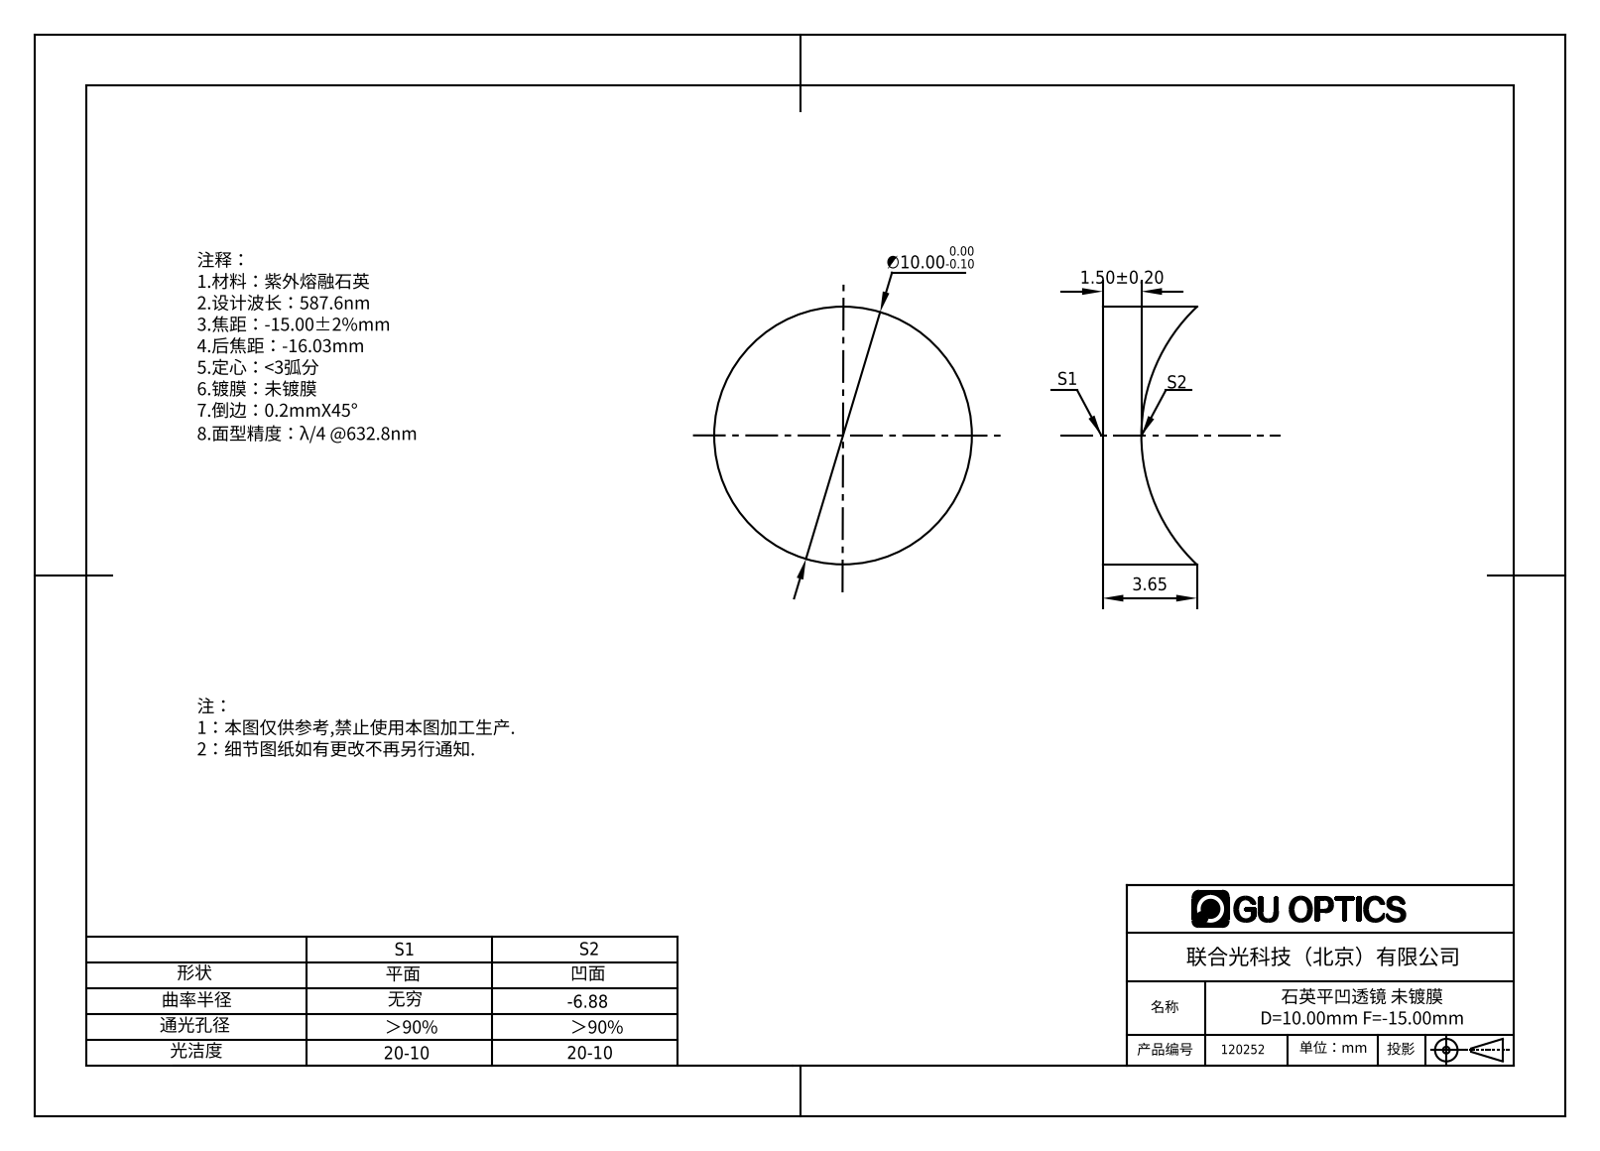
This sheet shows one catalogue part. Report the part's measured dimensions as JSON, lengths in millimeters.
{"part_name": "120252", "step_written_by": "SolidWorks 2016 (AUTOMOTIVE_DESIGN)", "units": "millimeters", "bodies": {"solids": 1, "faces": 5, "planar": 1, "cylindrical": 2, "other": 2}, "overall_size": [10, 10, 3.65], "volume_mm3": 197, "surface_area_mm2": 286, "round_bosses_or_shafts": [[10, 1]]}
